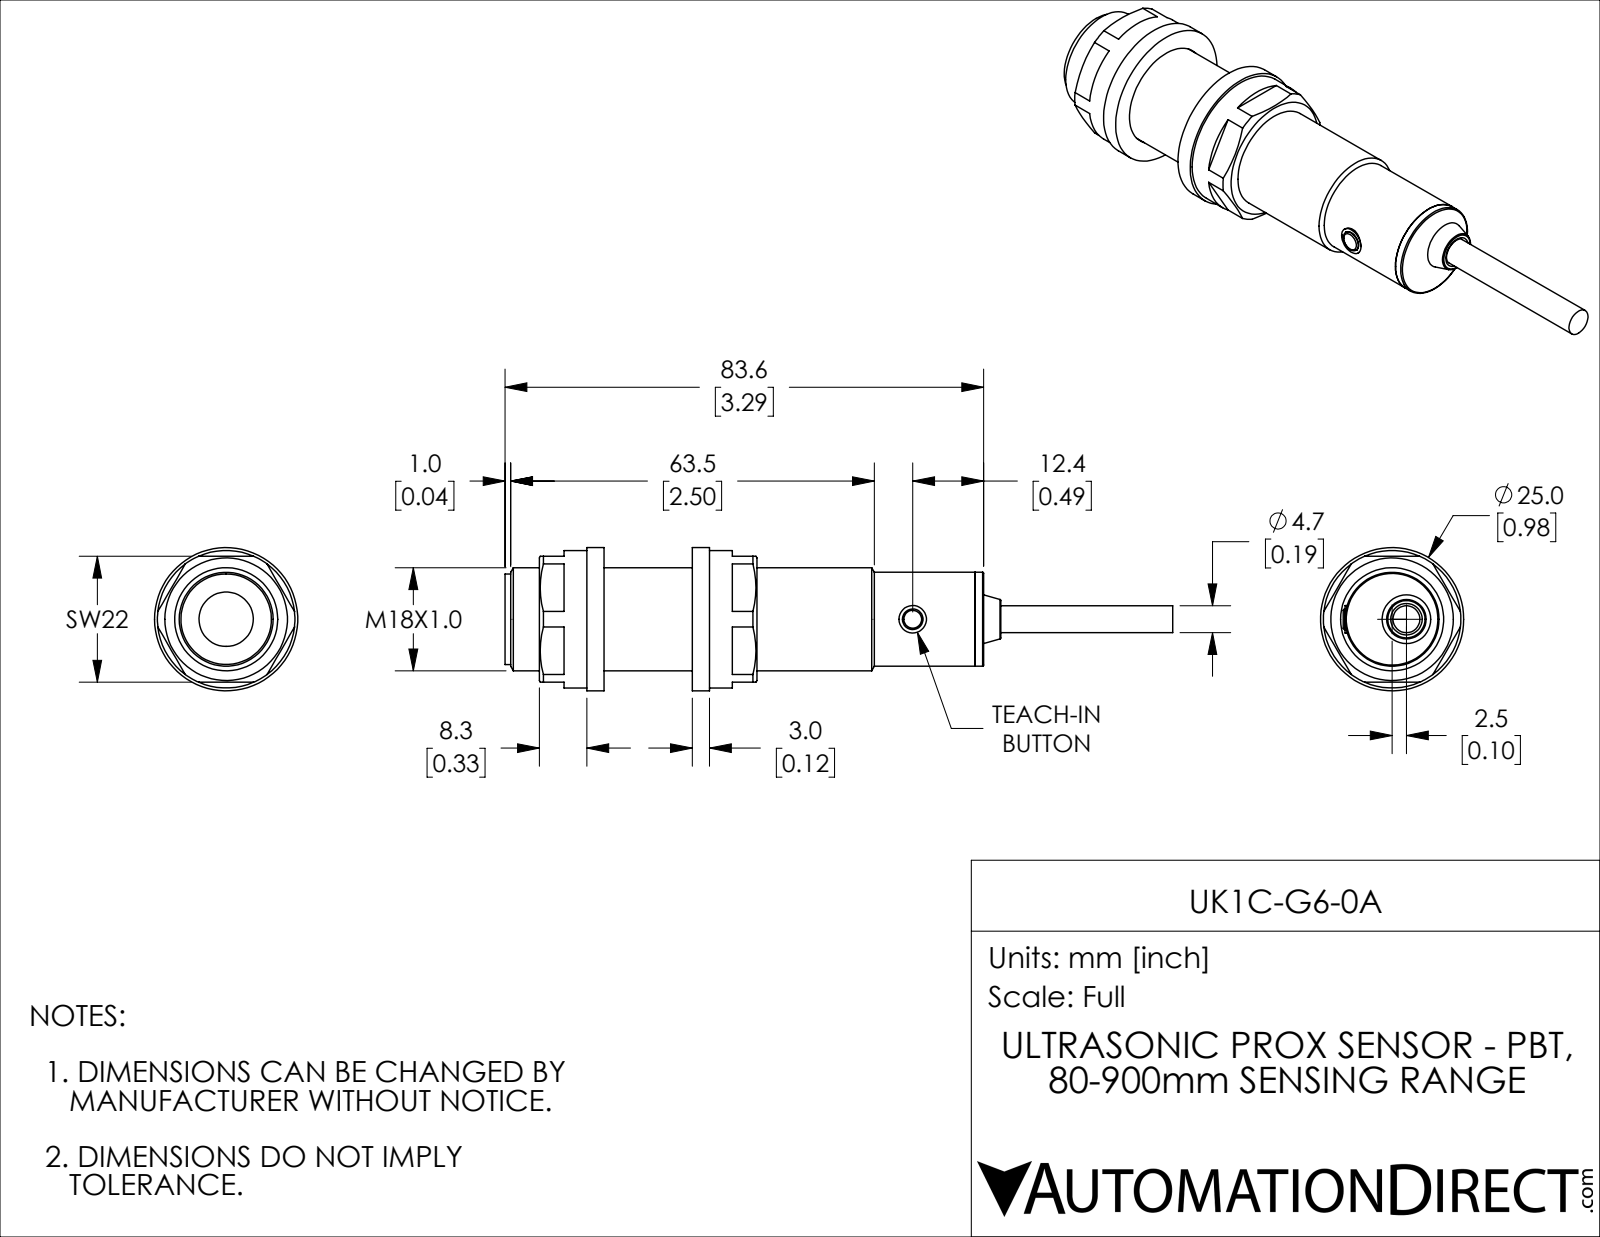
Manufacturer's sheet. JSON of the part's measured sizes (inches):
{"part_name": "UK1C-G6-0A", "step_written_by": "SolidWorks 2018 (AUTOMOTIVE_DESIGN)", "units": "inches", "bodies": {"solids": 10, "faces": 107, "planar": 49, "cylindrical": 40, "other": 18}, "overall_size": [4.591, 0.984, 0.984], "volume_in3": 1.539, "surface_area_in2": 17.7, "round_holes": [[0.185, 2], [0.142, 1], [0.374, 1], [0.709, 1], [0.717, 1]], "round_bosses_or_shafts": [[0.984, 1], [0.945, 1], [0.646, 1], [0.622, 1], [0.213, 1], [0.189, 1]], "face_to_face_distances": [0.118, 0.724, 0.843, 2.669, 1.827, 0.524, 1.366, 3.193, 0.642, 2.551], "hole_center_spacings": [0.098]}
